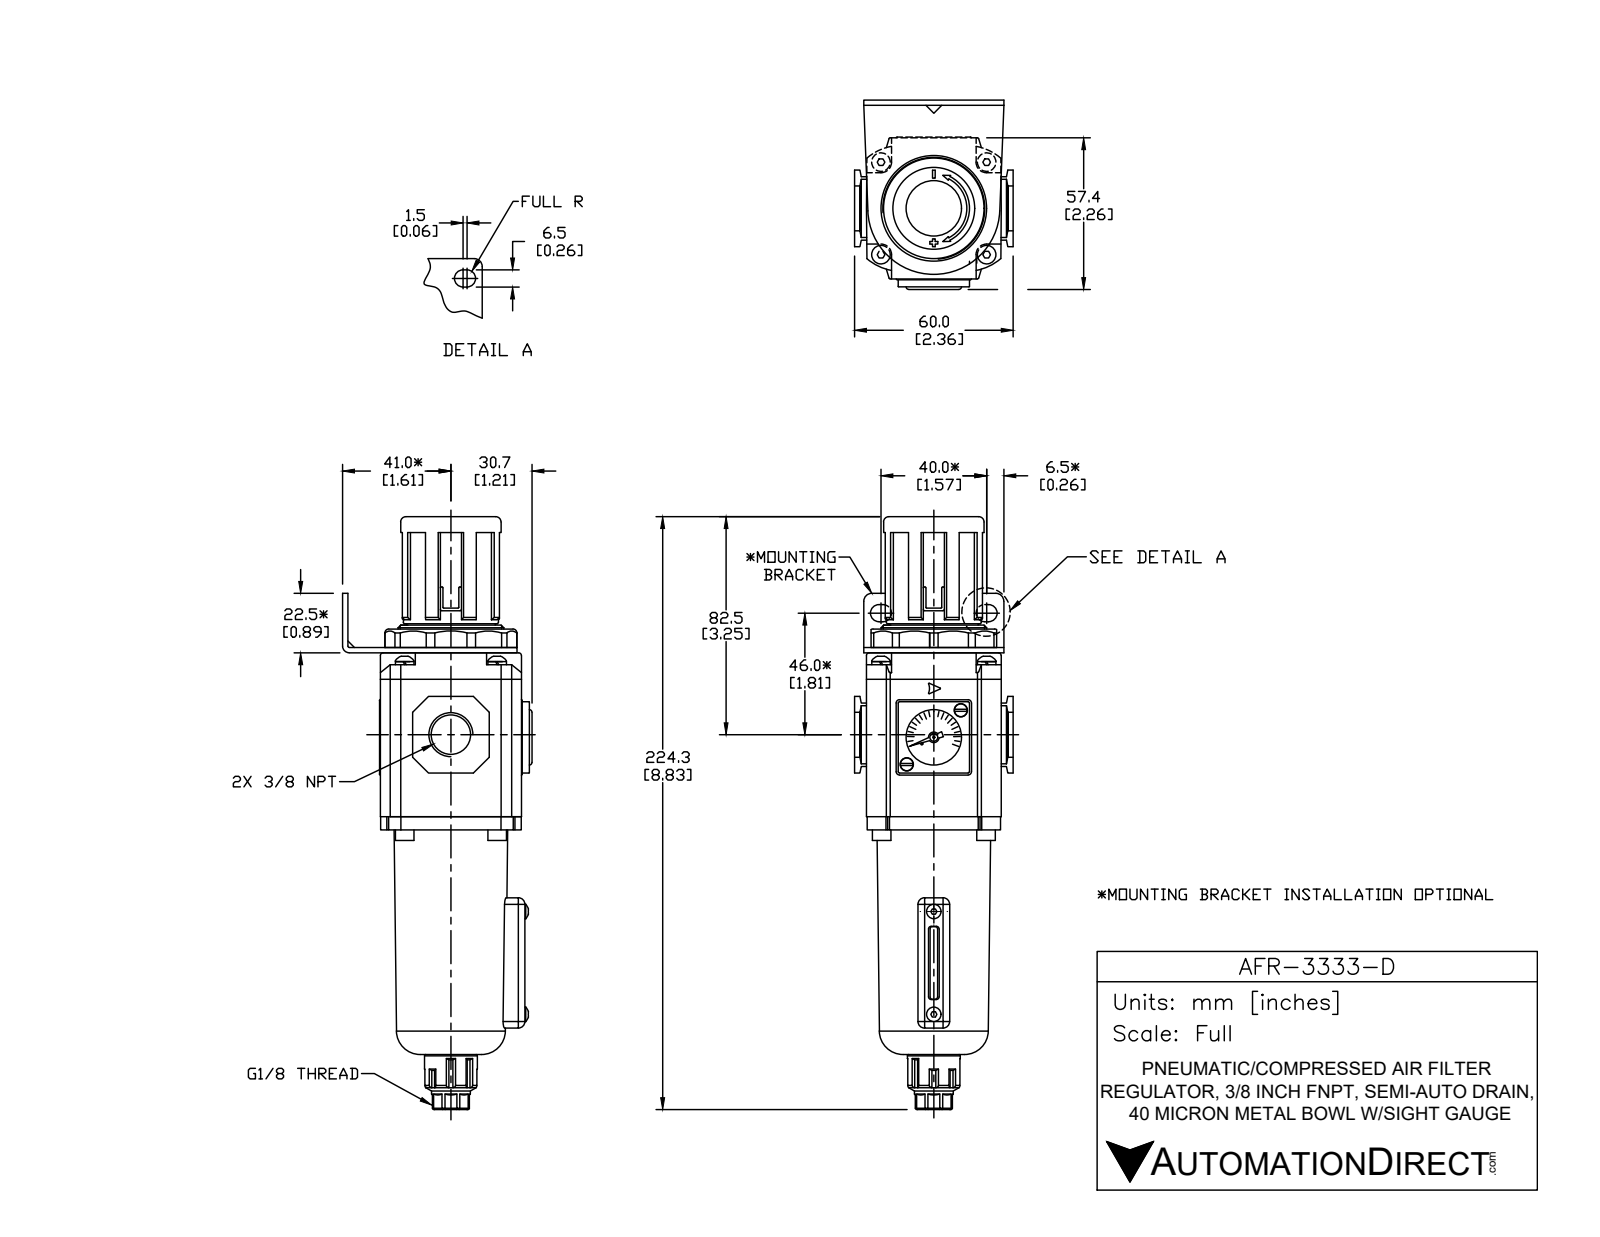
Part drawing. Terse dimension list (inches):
name: AFR-3333-D
written by: SolidWorks 2015 (CONFIG_CONTROL_DESIGN)
unit: in
bodies: 16 solids, 686 faces (418 planar, 181 cylindrical, 87 other)
size: 8.831 × 2.835 × 2.362
volume: 21.91 in³; area: 100.4 in²
holes: 6× ⌀0.118, 1× ⌀0.079, 1× ⌀0.244, 1× ⌀0.562, 1× ⌀0.827, 1× ⌀1.181, 1× ⌀1.26
bosses: 6× ⌀0.217, 4× ⌀0.276, 2× ⌀0.106, 1× ⌀1.575, 1× ⌀1.496, 1× ⌀1.417, 1× ⌀1.319, 1× ⌀0.806
rounds: 16× R0.039, 10× R0.047, 8× R0.051, 8× R0.098, 8× R0.374, 8× R0.783, 6× R0.02, 6× R0.128
face distances: 0.079, 2.441, 2.52, 2.102, 2.008, 0.039, 2.185, 2.063, 2.638, 0.177
hole spacings: 1.046, 0.571, 1.378, 1.575, 2.093, 1.141
